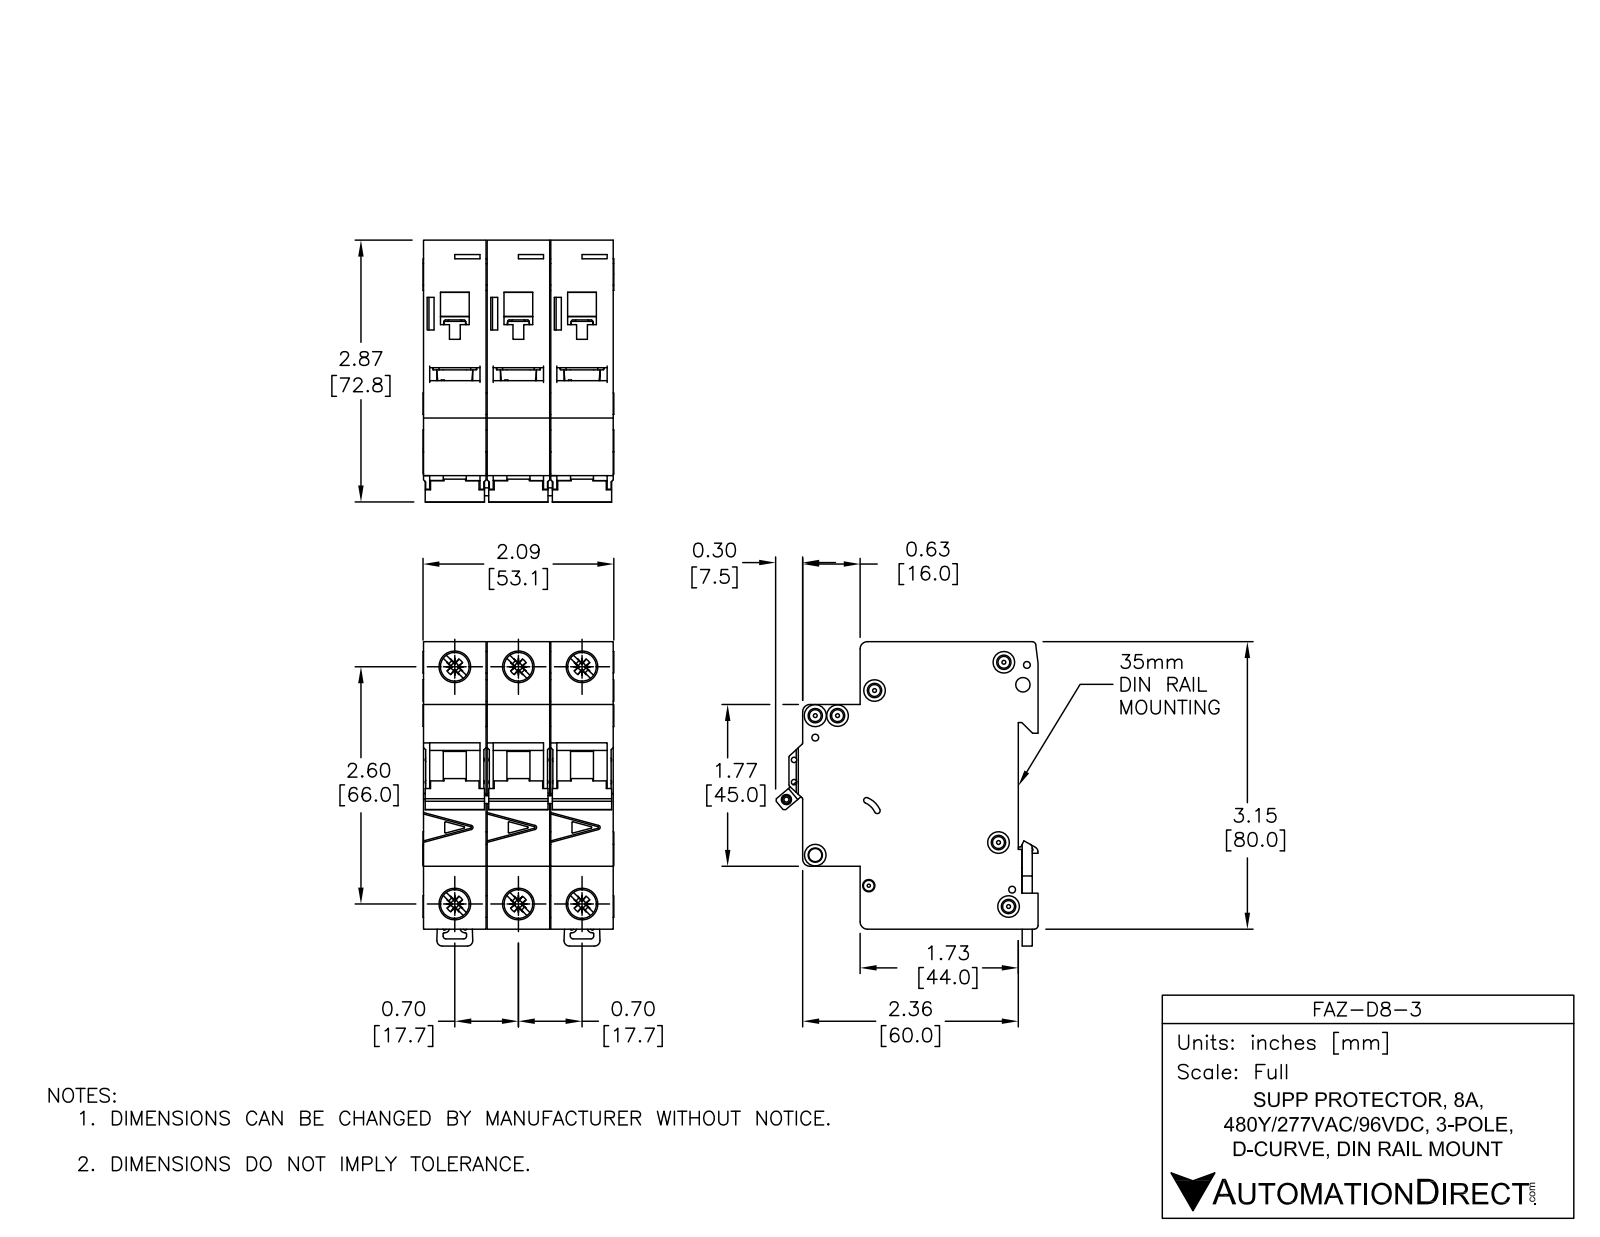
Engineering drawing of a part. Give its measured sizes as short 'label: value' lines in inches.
name: FAZ-D8-3
written by: SolidWorks 2014 (AUTOMOTIVE_DESIGN)
unit: in
bodies: 11 solids, 1650 faces (697 planar, 590 cylindrical, 363 other)
size: 3.338 × 2.876 × 2.091
volume: 13.71 in³; area: 89.98 in²
holes: 6× ⌀0.142, 4× ⌀0.323, 3× ⌀0.075, 2× ⌀0.043, 2× ⌀0.059, 2× ⌀0.157, 2× ⌀0.281, 1× ⌀0.085, 1× ⌀0.087, 1× ⌀0.1, 1× ⌀0.13, 1× ⌀0.134
bosses: 4× ⌀0.236, 3× ⌀0.098, 2× ⌀0.323
rounds: 68× R0.01, 25× R0.02, 12× R0.039, 12× R0.079, 11× R0.008, 3× R0.071, 2× R0.031, 2× R0.118
face distances: 0.697, 0.689, 1.394, 1.386, 2.083, 0.705, 3.129, 0.217, 1.949, 1.732
hole spacings: 0.697, 2.69, 2.598, 0.244, 0.537, 1.394, 2.948, 0.189
